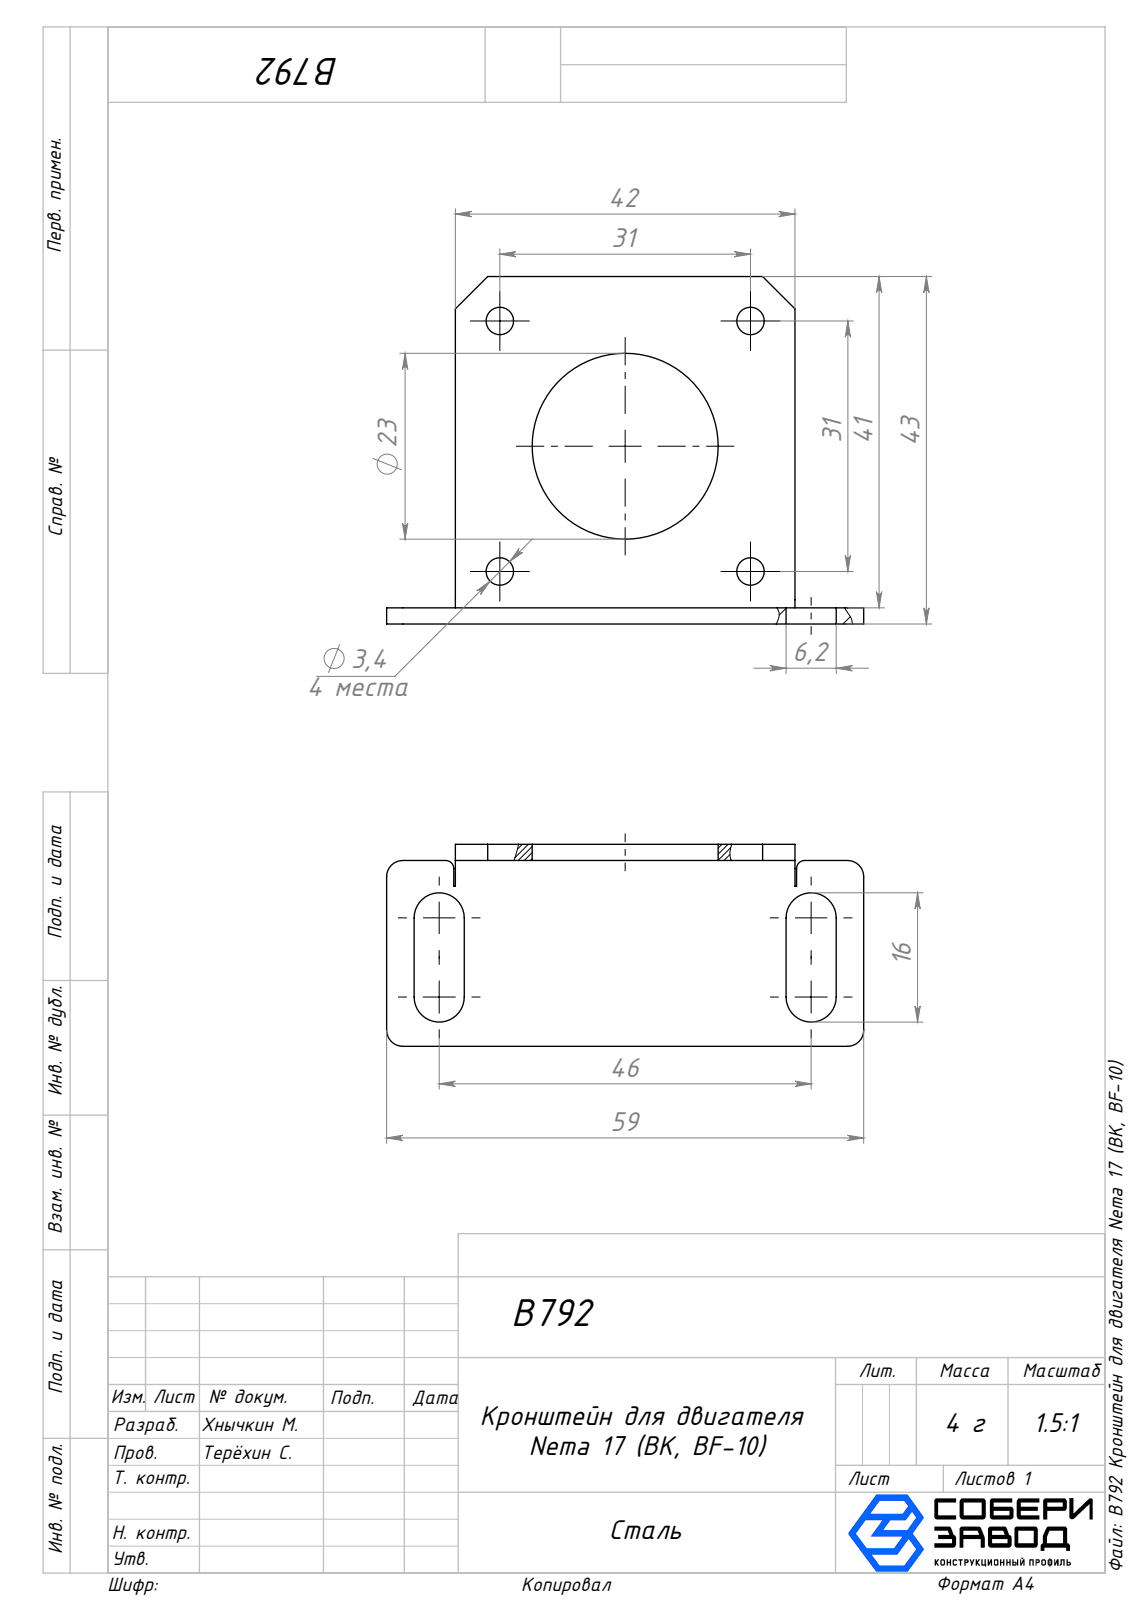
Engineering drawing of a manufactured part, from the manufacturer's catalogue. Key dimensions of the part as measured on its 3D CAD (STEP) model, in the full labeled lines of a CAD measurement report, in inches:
Part name (STEP PRODUCT): B792 Кронштейн для двигателя Nema 17 (BK, BF-10)
STEP written by: SolidWorks 2025 (AUTOMOTIVE_DESIGN)
Units: inches
Bodies: 1 solid, 48 faces (26 planar, 22 cylindrical, 0 other)
Overall size (bounding box): 2.323 × 1.693 × 0.984
Volume: 0.302 in³ · Surface area: 9.044 in²
Round holes (diameter × count): ⌀0.134 ×4, ⌀0.906 ×1
Partial cylindrical surfaces — rounded edges, fillets, slot ends (radius × count): R0.079 ×4, R0.122 ×4, R0.039 ×3, R0.118 ×1
Main face-to-face distances: 0.079, 0.984, 0.906, 1.654, 0.335, 1.988, 1.693, 1.614, 0.134, 0.378
Hole centre spacings: 0.863, 1.22, 1.726
